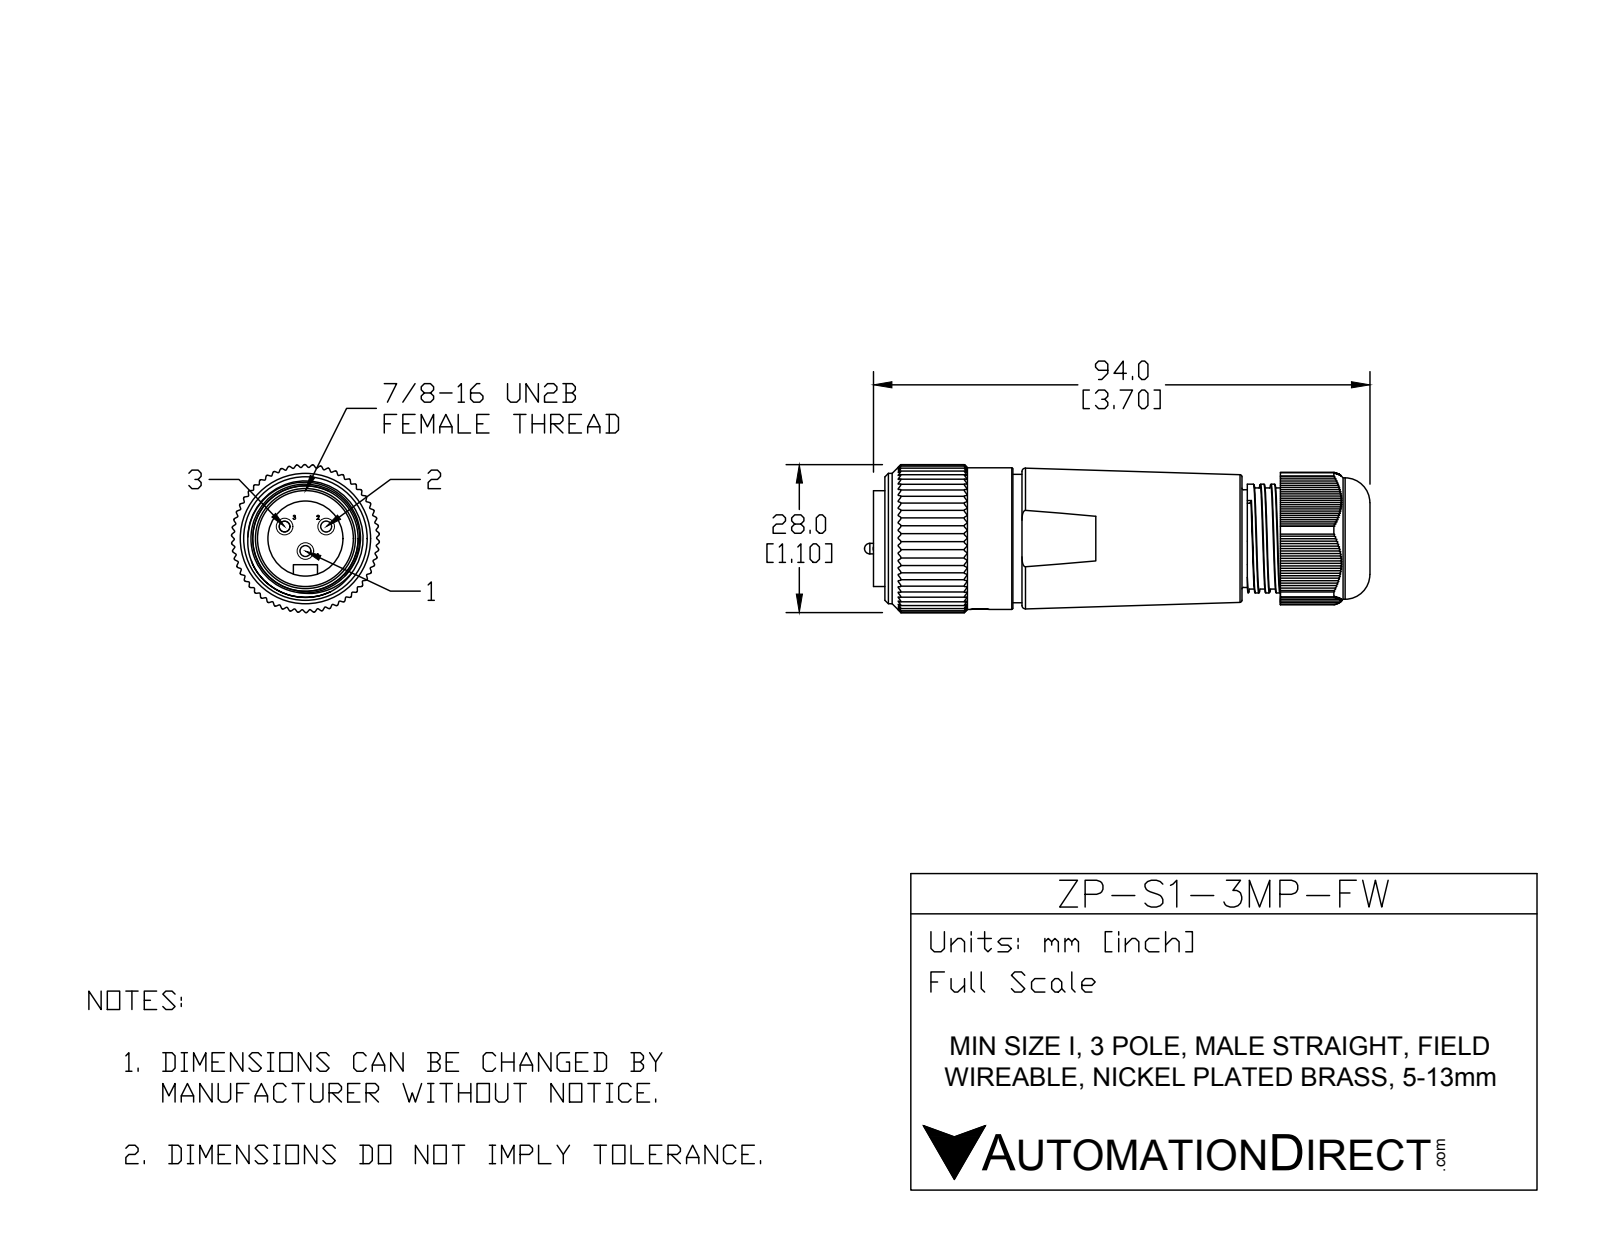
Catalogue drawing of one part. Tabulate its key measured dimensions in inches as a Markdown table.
| quantity | value |
| --- | --- |
| part name | MIN-3MP-FW |
| STEP written by | SolidWorks 2015 (AUTOMOTIVE_DESIGN) |
| units | inches |
| bodies | 1 solid, 833 faces (445 planar, 322 cylindrical, 66 other) |
| overall size | 3.746 × 1.102 × 1.102 |
| volume | 2.67 in³ |
| surface area | 19.17 in² |
| round holes (diameter × count) | 0.138 × 1, 0.53 × 1, 0.56 × 1, 0.81 × 1, 1 × 1 |
| round bosses / shafts (diameter × count) | 0.124 × 3, 0.079 × 3, 1.055 × 1, 0.972 × 1, 0.957 × 1, 0.945 × 1, 0.905 × 1, 0.811 × 1 |
| partial cylindrical surfaces (radius × count) | 0.01 × 116, 0.008 × 58, 0.09 × 1, 0.521 × 1, 0.551 × 1 |
| main face-to-face distances | 0.014, 0.028, 0.043, 0.746, 2.767, 0.057, 0.25, 0.652, 0.638, 0.624 |
